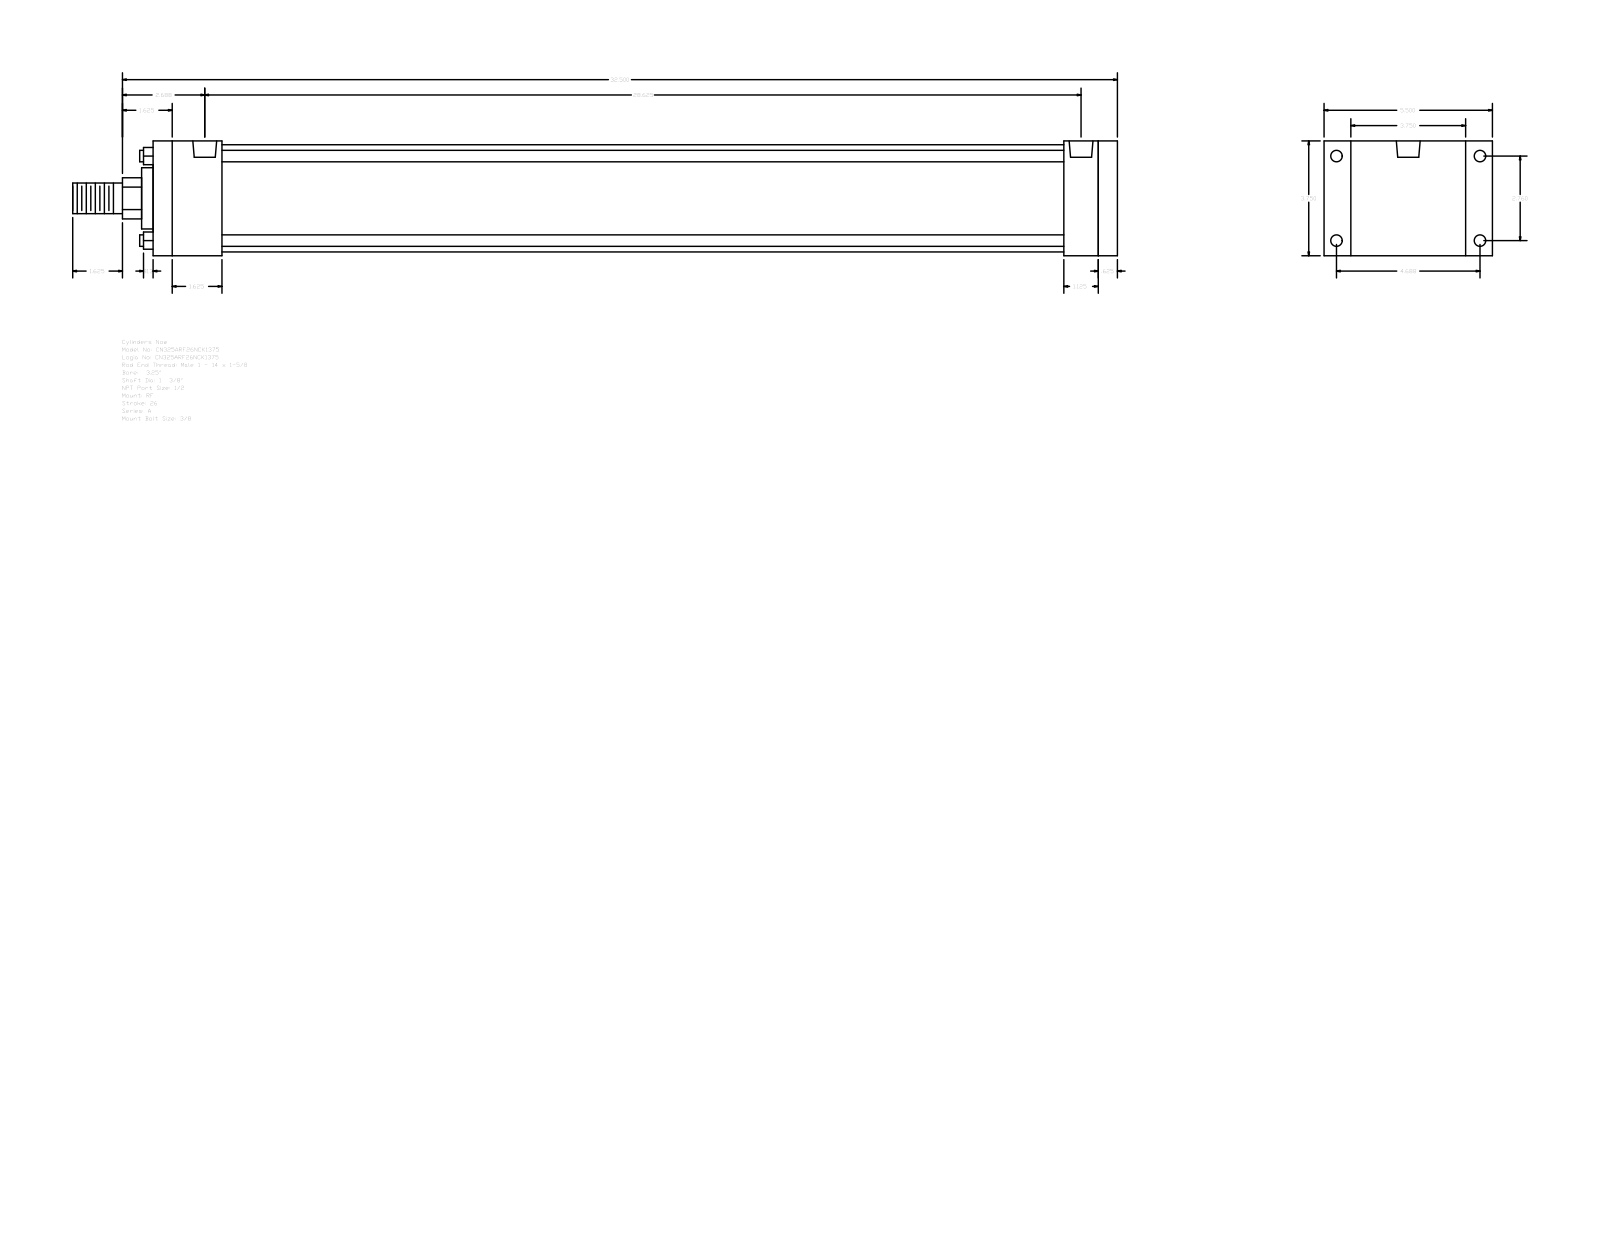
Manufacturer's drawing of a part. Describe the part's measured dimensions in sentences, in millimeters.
The part is named "A_RF__0325_1.375". Its 3-D file was written by "GSSL Pune (CONFIG_CONTROL_DESIGN)". It is 0 solids with 92 faces: 64 planar, 28 cylindrical and 0 other. Overall it measures 866.77 by 139.7 by 95.25 millimeters. Round holes: 4 of diameter 8.73, 4 of diameter 9.53, 2 of diameter 19.77. Round bosses or shafts: 4 of diameter 9.53, 1 of diameter 88.9, 1 of diameter 50.8, 1 of diameter 34.92, 1 of diameter 25.4. Partial cylindrical surfaces (rounded edges, fillets, slot ends): 1 of radius 17.06. The main face-to-face distances are 95.24, 800.1, 15.88, 784.22, 57.15, 22.23, 117.47, 755.65, 28.57, 44.45. The hole center spacings are 3.18, 70.1, 119.06, 138.16, 720.72, 723.9, 727.08.
